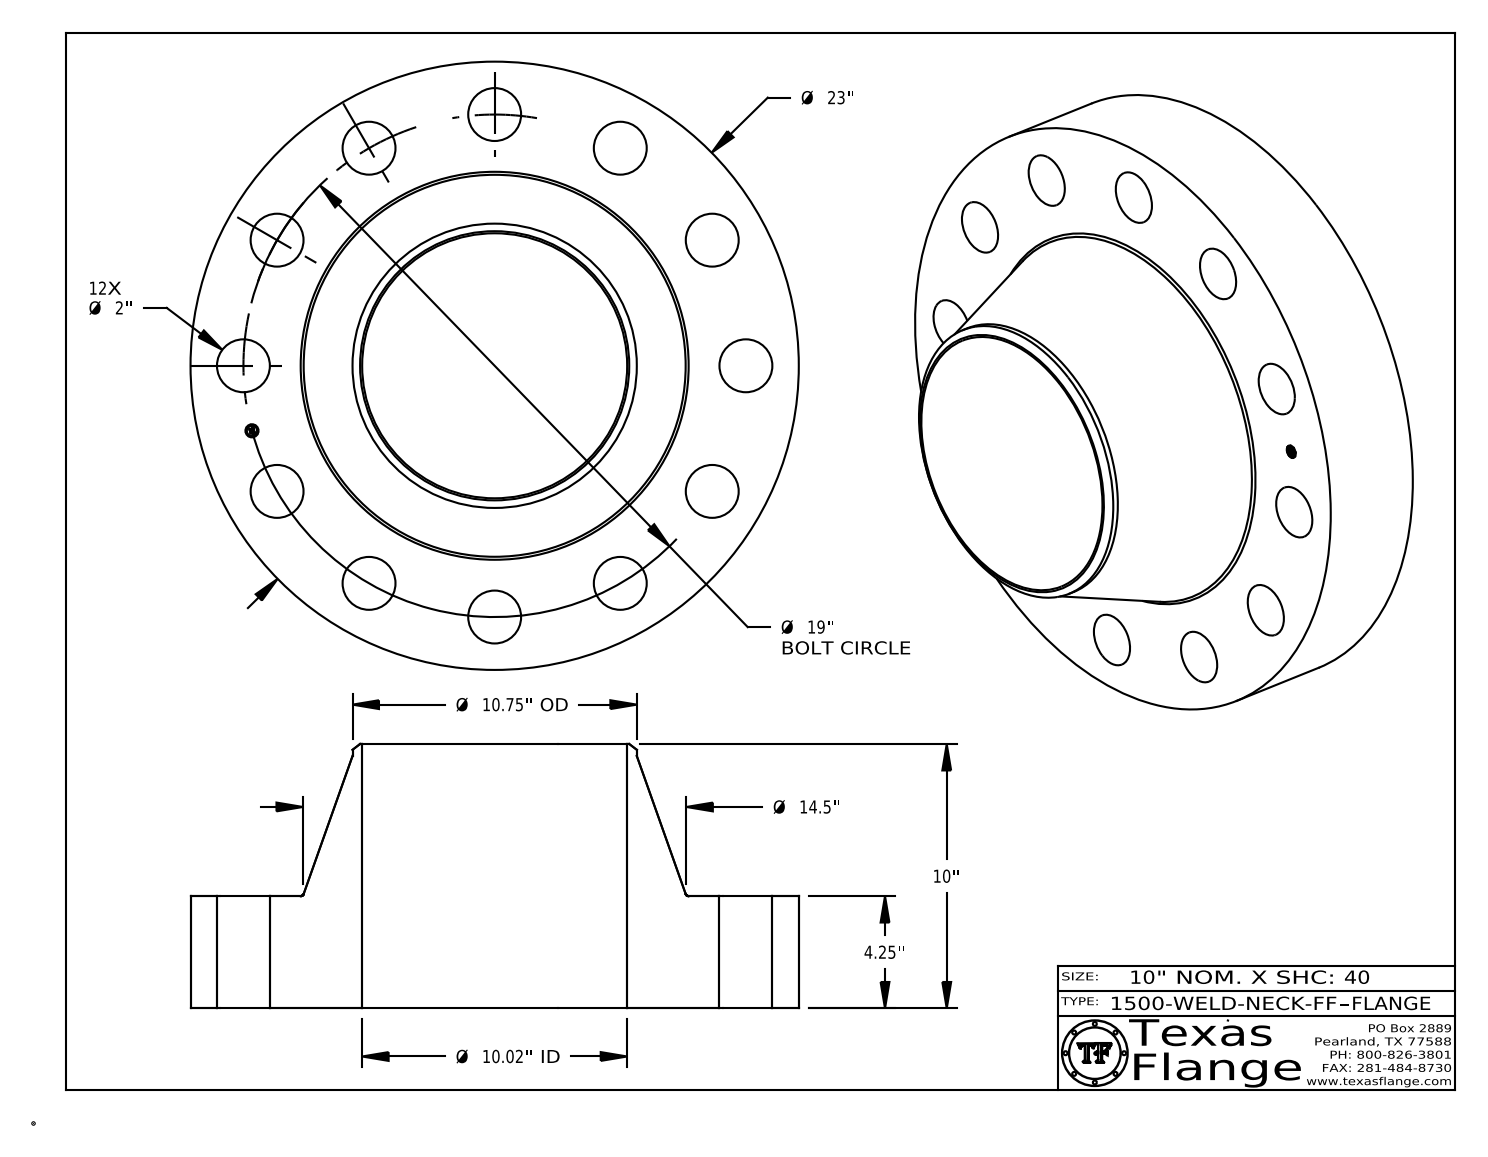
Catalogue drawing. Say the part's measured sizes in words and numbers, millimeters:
The part is named "1500-WELD-NECK-FF". Its 3-D file was written by "CATIA V5 STEP AP214 (AUTOMOTIVE_DESIGN)". It is 1 solid with 424 faces: 368 planar, 50 cylindrical and 6 other. Overall it measures 584.2 by 584.2 by 254 millimeters. Its volume is 24 990 000 cubic millimeters and its surface area 1 095 000 square millimeters. Round holes: 12 of diameter 50.8, 1 of diameter 12.6, 1 of diameter 254.5. Round bosses or shafts: 8 of diameter 0.8, 1 of diameter 584.2, 1 of diameter 273.1, 1 of diameter 9.9. The main face-to-face distances are 108, 254, 146.1, 107.6, 0.4, 146.4, 3.8, 3.7, 0.7, 2.4. The hole center spacings are 241.3, 341.2, 417.9, 466.1, 124.9, 482.6, 124.9, 382.9.
